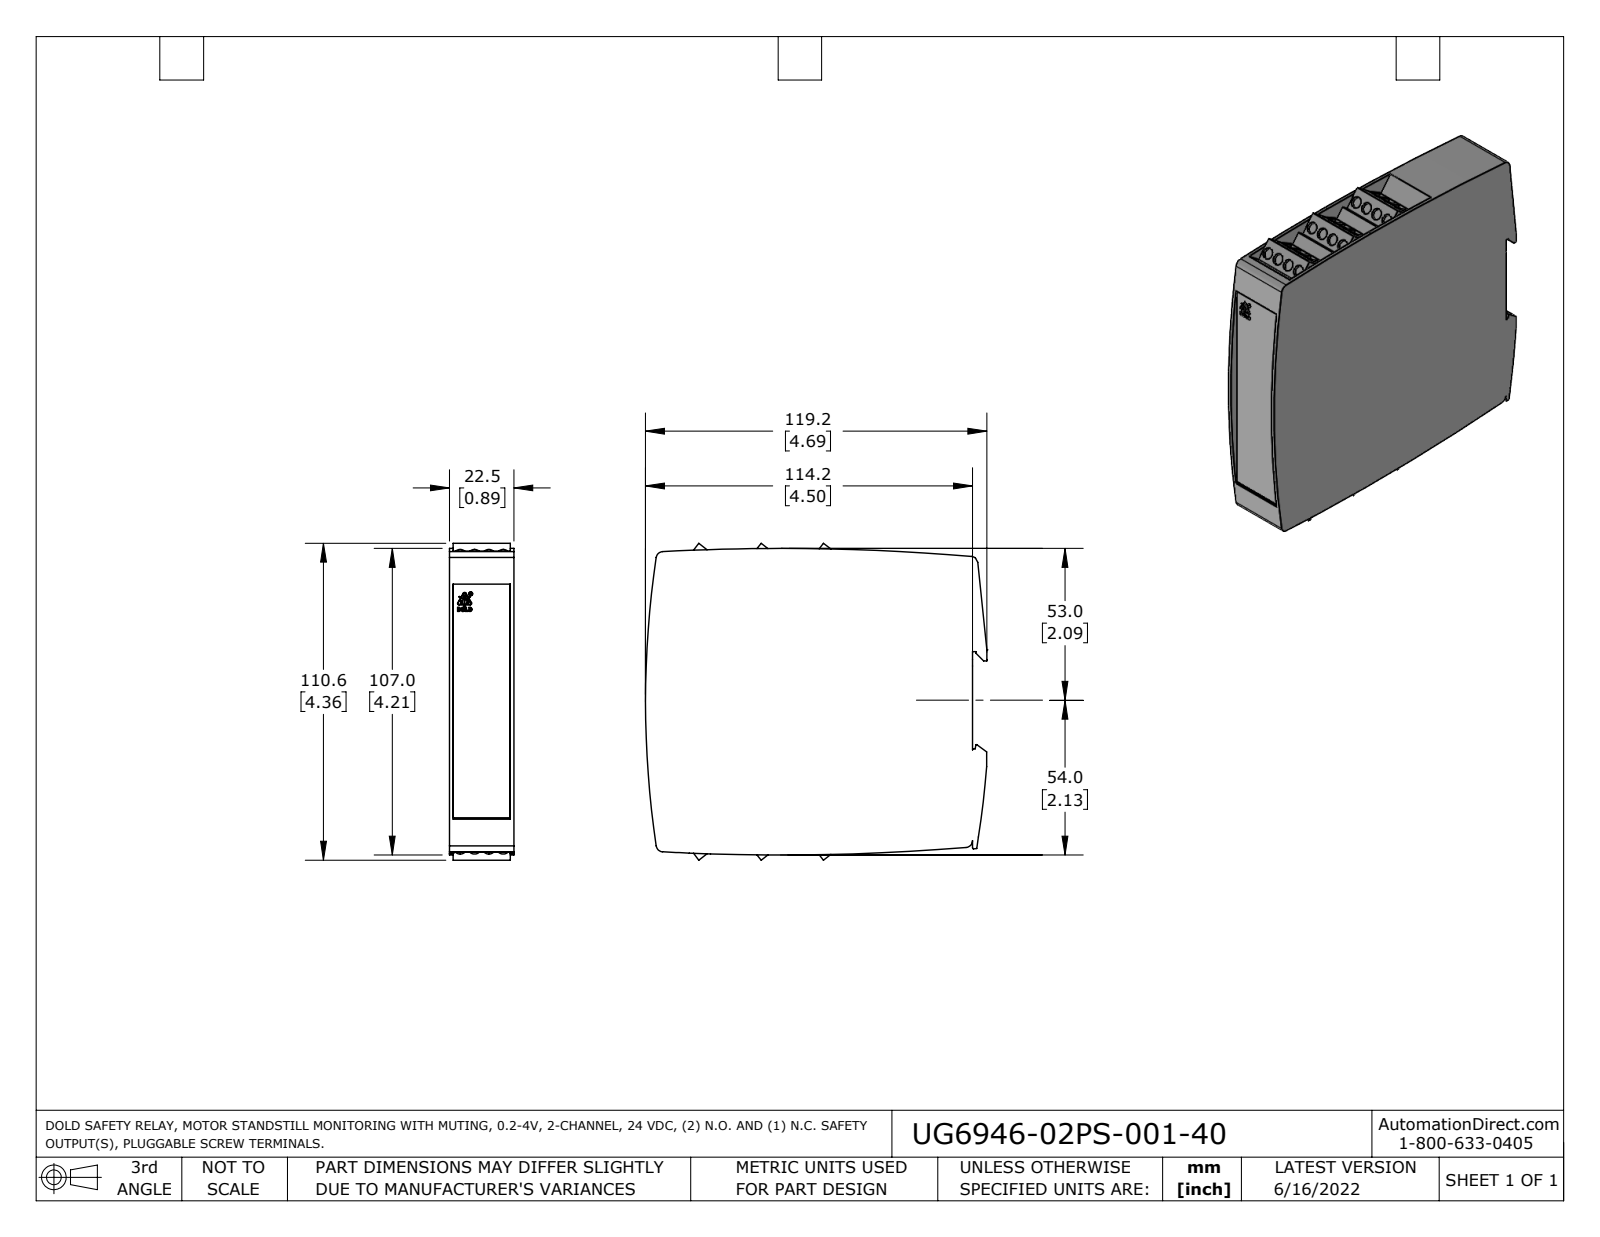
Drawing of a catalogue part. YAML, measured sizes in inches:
part_name: "UG6946-02PS-001-40_Default"
step_written_by: "SolidWorks 2021 (CONFIG_CONTROL_DESIGN)"
units: inches
bodies: {solids: 1, faces: 666, planar: 570, cylindrical: 95, other: 1}
overall_size: [4.693, 4.355, 0.886]
volume: 16
surface_area: 58.45
round_holes:
  - {diameter: 0.157, count: 24}
  - {diameter: 0.053, count: 1}
round_bosses_or_shafts:
  - {diameter: 0.049, count: 1}
partial_cylinders:
  - {radius: 0.004, count: 12}
  - {radius: 0.012, count: 12}
  - {radius: 0.094, count: 7}
  - {radius: 0.005, count: 6}
  - {radius: 0.004, count: 4}
  - {radius: 31.496, count: 4}
  - {radius: 0.021, count: 3}
  - {radius: 0.012, count: 2}
face_to_face_distances: [0.886, 0.049, 0.837, 0.528, 0.675, 4.379, 0.787, 1.35, 1.056, 0.566]
hole_center_spacings: [0.197, 0.394, 0.563, 0.563, 1.074, 0.528, 0.528, 0.658]
